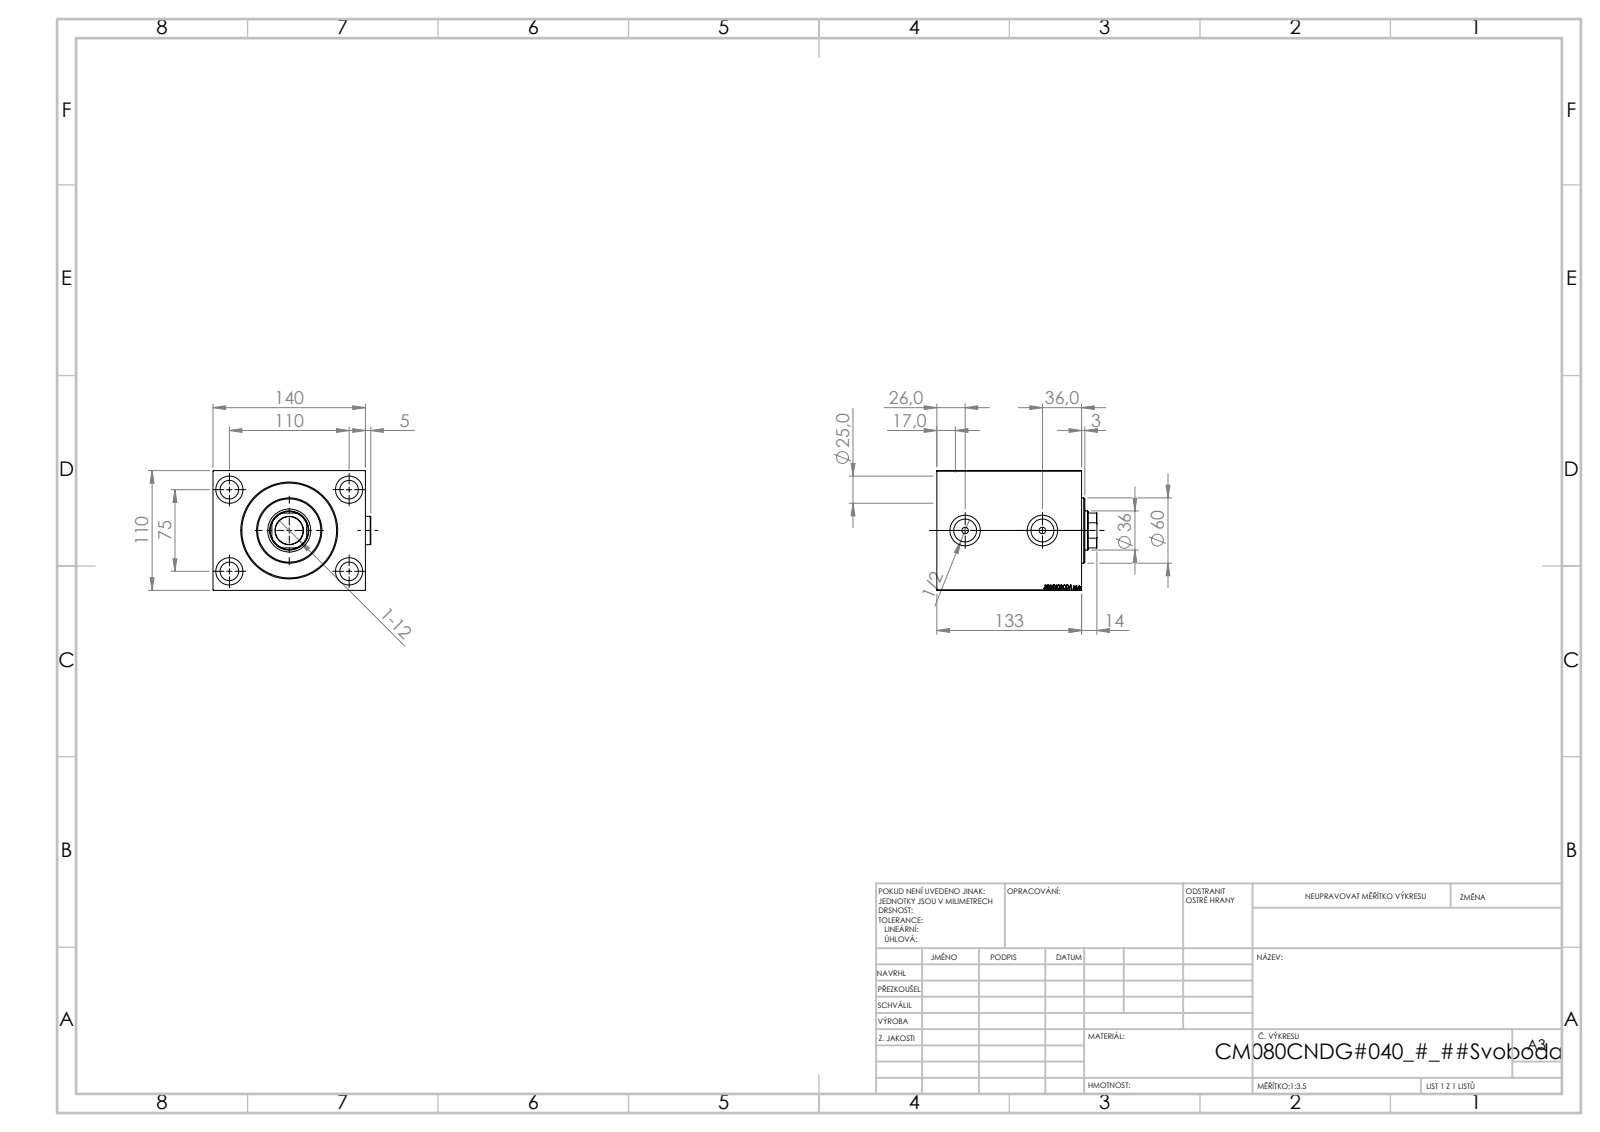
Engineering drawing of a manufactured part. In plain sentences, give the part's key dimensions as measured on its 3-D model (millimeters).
The part is named "V450CM_VC_B; V450CM_C_VCP; V450CM_C_Body; Zatka_OIL_PORT". Its 3-D file was written by "SolidWorks 2019 (CONFIG_CONTROL_DESIGN)". It is 5 solids with 919 faces: 443 planar, 78 cylindrical and 398 other. Overall it measures 147 by 144.9 by 110 millimeters. Its volume is 1 716 000 cubic millimeters and its surface area 213 843 square millimeters. Round holes: 4 of diameter 17, 4 of diameter 25, 2 of diameter 6, 2 of diameter 20.96, 2 of diameter 28, 1 of diameter 25.5, 1 of diameter 36, 1 of diameter 39.5, 1 of diameter 80, 1 of diameter 82, 1 of diameter 87. Round bosses or shafts: 2 of diameter 26, 1 of diameter 60. Partial cylindrical surfaces (rounded edges, fillets, slot ends): 1 of radius 17.5. The main face-to-face distances are 110, 140, 133, 112, 21, 119, 14, 98, 54, 40. The hole center spacings are 66.57, 75, 110, 133.14, 71.
